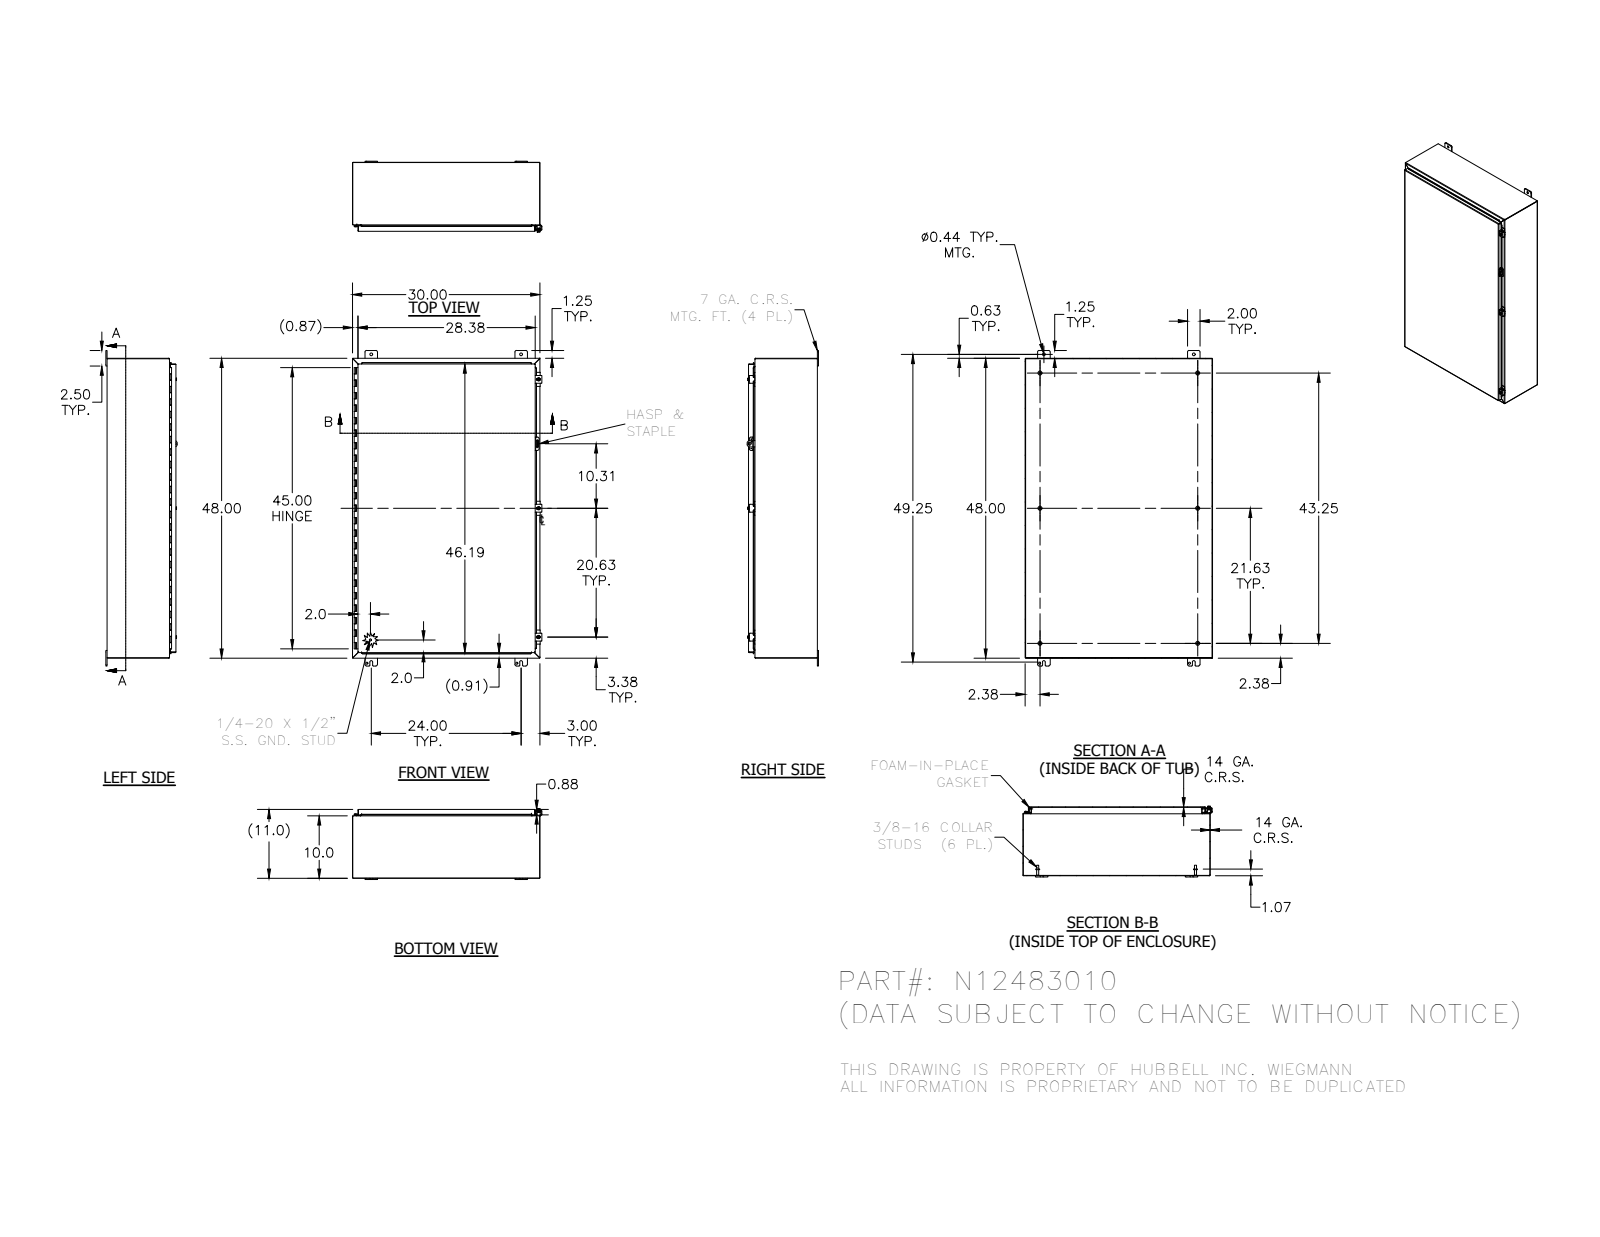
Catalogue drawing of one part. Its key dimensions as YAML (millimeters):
part_name: "N12483010; 34840; 38413; N123010TB (+8 more)"
step_written_by: "Autodesk Inventor 2012 (AUTOMOTIVE_DESIGN)"
units: millimeters
bodies: {solids: 36, faces: 1233, planar: 726, cylindrical: 386, other: 121}
overall_size: [1282.7, 769.9, 289.8]
volume: 6227000
surface_area: 6486000
round_holes:
  - {diameter: 8, count: 4}
  - {diameter: 11.1, count: 4}
  - {diameter: 2.8, count: 3}
  - {diameter: 5.4, count: 3}
  - {diameter: 7.1, count: 3}
  - {diameter: 7.6, count: 3}
  - {diameter: 3.2, count: 1}
  - {diameter: 4, count: 1}
  - {diameter: 12.7, count: 1}
round_bosses_or_shafts:
  - {diameter: 15.9, count: 6}
  - {diameter: 8.4, count: 6}
  - {diameter: 6.4, count: 5}
  - {diameter: 13.2, count: 3}
  - {diameter: 12.7, count: 3}
  - {diameter: 8.9, count: 3}
  - {diameter: 8.6, count: 1}
  - {diameter: 3, count: 1}
partial_cylinders:
  - {radius: 0.8, count: 39}
  - {radius: 3.2, count: 27}
  - {radius: 6.4, count: 27}
  - {radius: 0.8, count: 21}
  - {radius: 2.7, count: 21}
  - {radius: 1.6, count: 15}
  - {radius: 2.5, count: 6}
  - {radius: 3.6, count: 6}
face_to_face_distances: [1.9, 278.4, 276.5, 280.2, 760.1, 1217.3, 758.2, 762, 252.1, 26.2]
hole_center_spacings: [40.5, 609.6, 1219.2, 1363.1, 20.1, 262.3, 593.3, 628.1]
